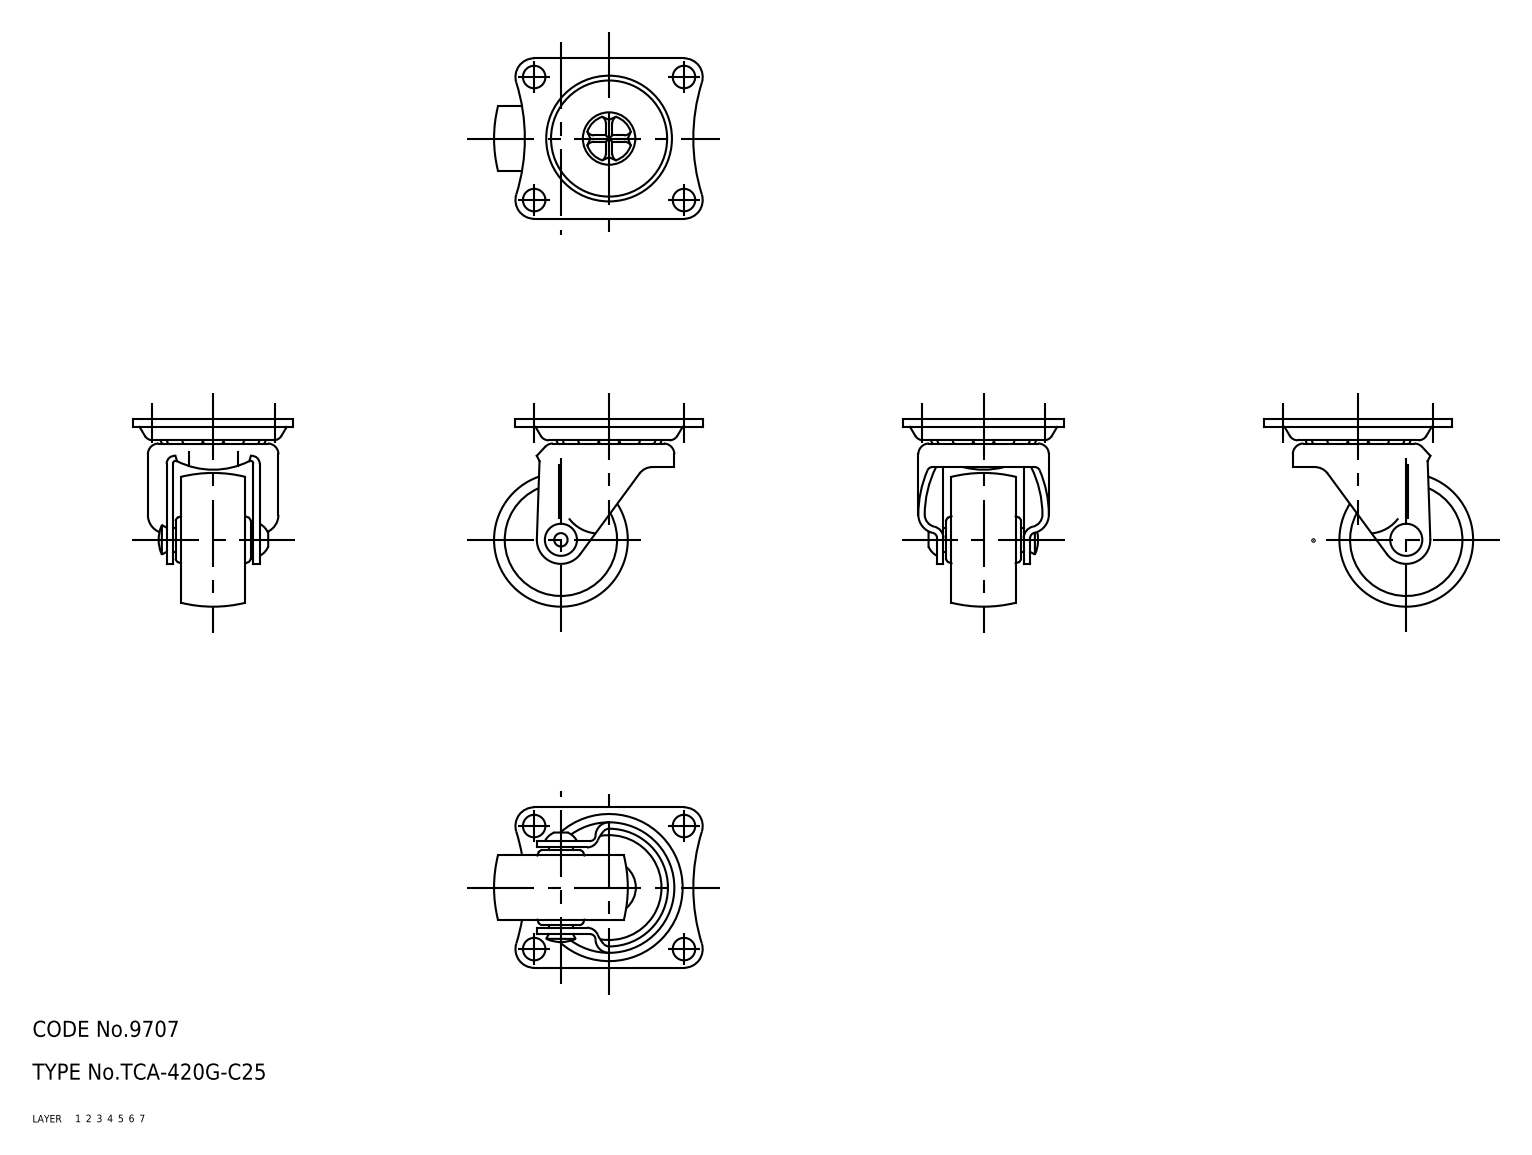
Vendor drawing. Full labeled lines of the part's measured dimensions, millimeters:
Part name (STEP PRODUCT): wheel; mounting plate; main shaft; axle (+1 more)
STEP written by: CADfix (AUTOMOTIVE_DESIGN)
Units: millimetres
Bodies: 5 solids, 230 faces (0 planar, 0 cylindrical, 230 other)
Overall size (bounding box): 39 × 35 × 30
Volume: 8 025 mm³ · Surface area: 8 432 mm²
